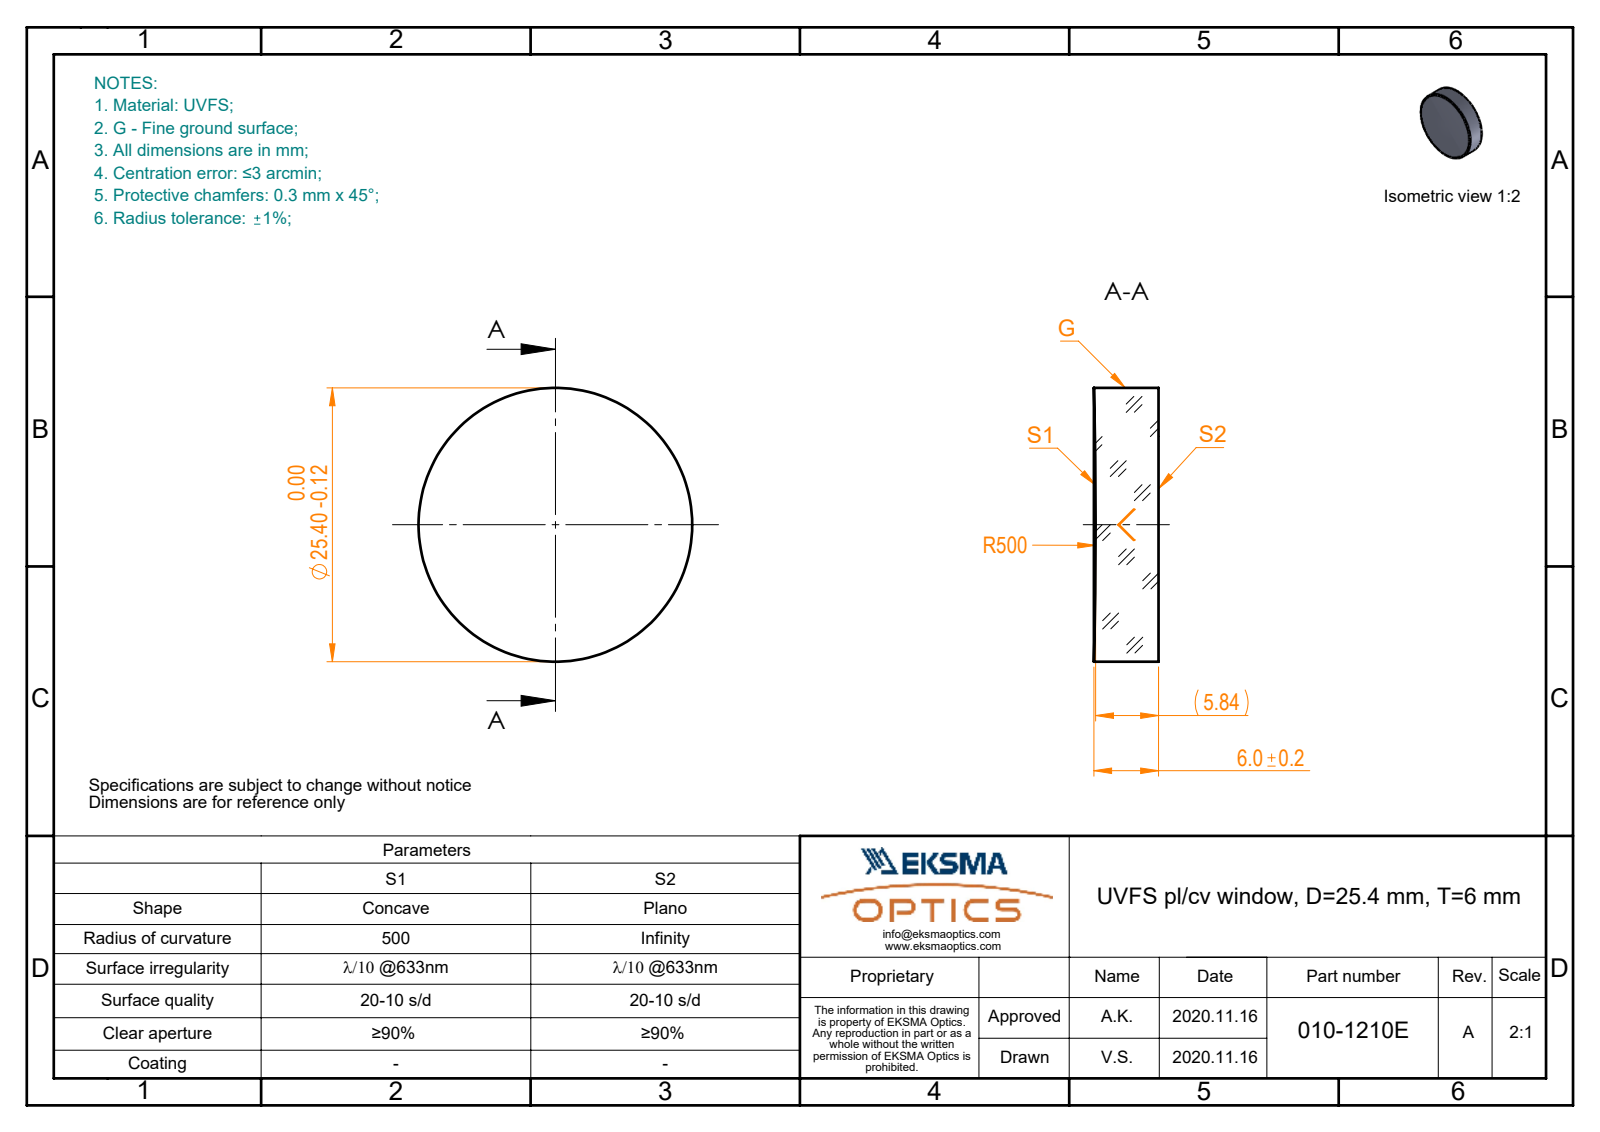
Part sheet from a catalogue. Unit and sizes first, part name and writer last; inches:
Units: inches
Overall size (bounding box): 1 × 1 × 0.236
Round bosses / shafts (diameter × count): ⌀1 ×1
Volume: 0.183 in³ · Surface area: 2.313 in²
Bodies: 1 solid, 5 faces (1 planar, 2 cylindrical, 2 other)
Part name (STEP PRODUCT): 010-1210E_UVFS_PCV_window
STEP written by: SolidWorks 2019 (CONFIG_CONTROL_DESIGN)
